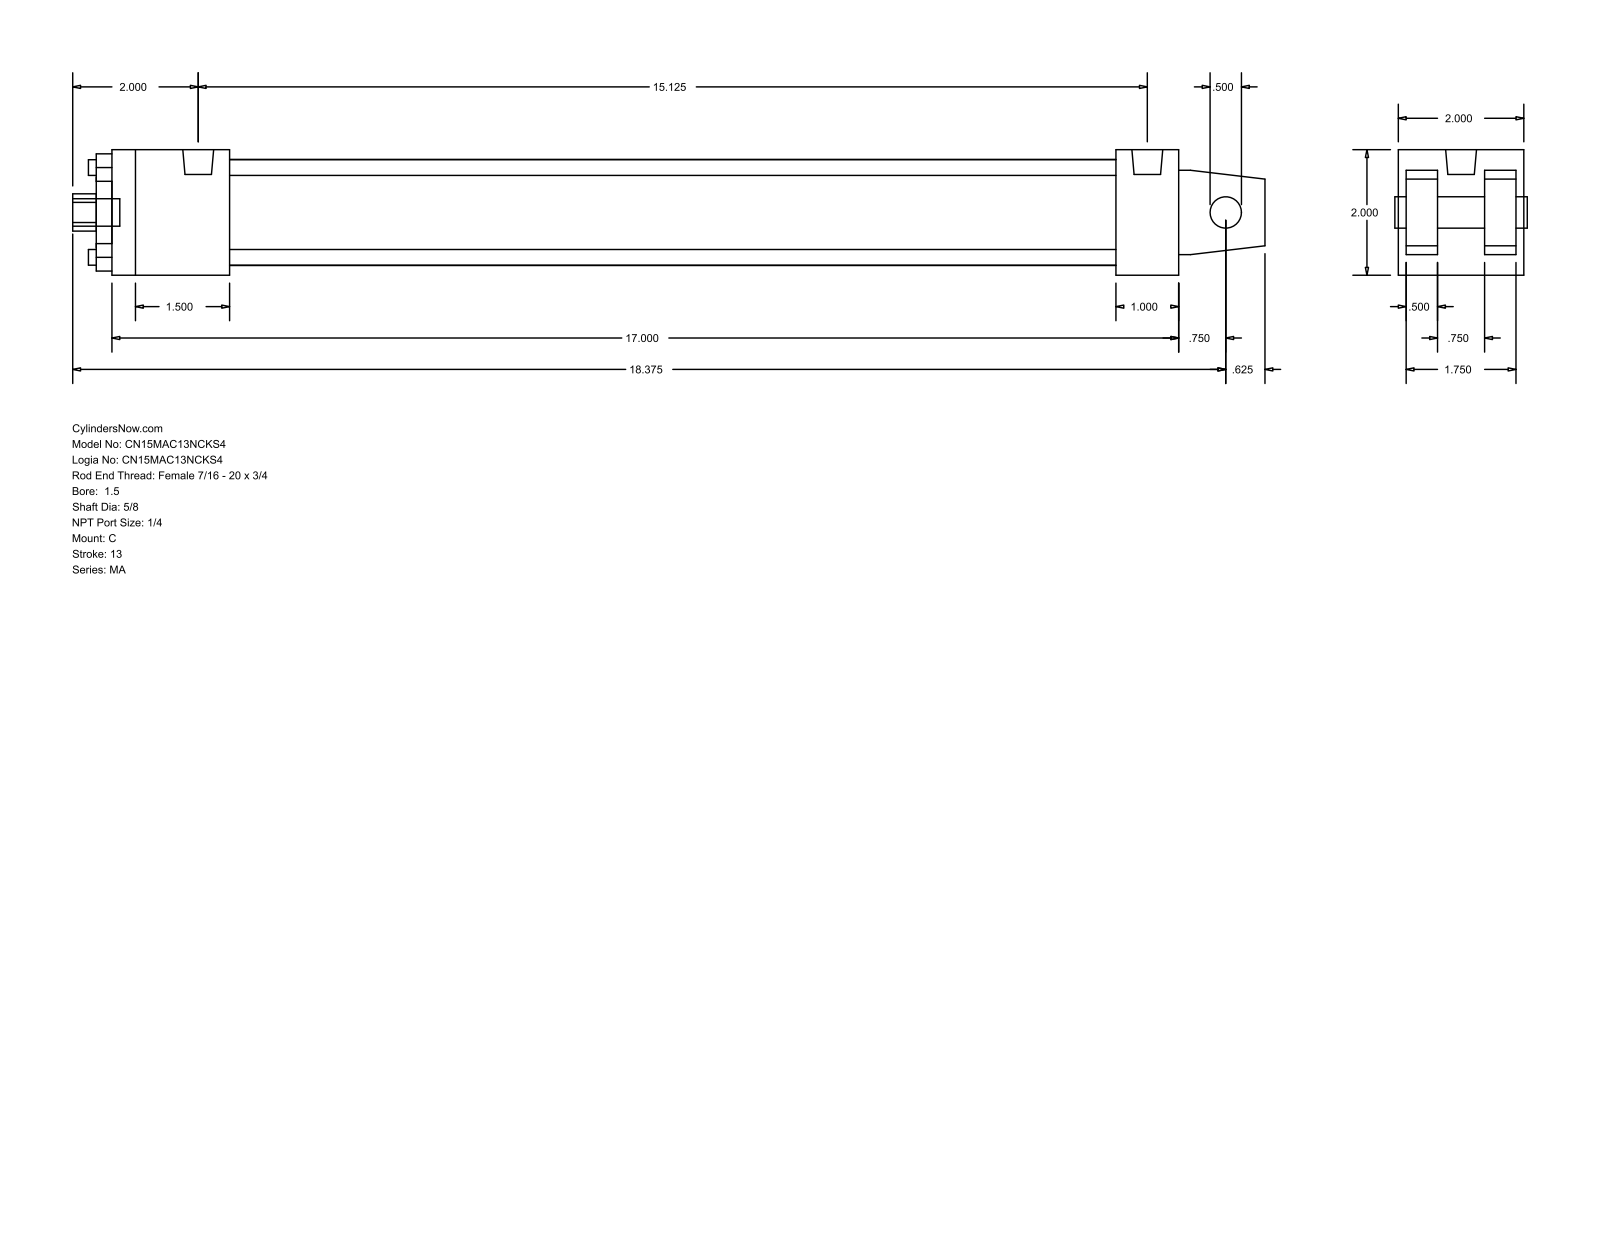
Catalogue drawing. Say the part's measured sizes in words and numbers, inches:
The part is named "MA_C__0150_0.625". Its 3-D file was written by "GSSL Pune (CONFIG_CONTROL_DESIGN)". It is 0 solids with 103 faces: 76 planar, 27 cylindrical and 0 other. Overall it measures 19 by 2 by 2 inches. Round holes: 4 of diameter 0.25, 1 of diameter 0.5, 1 of diameter 0.625, 1 of diameter 1.125, 1 of diameter 1.69. Round bosses or shafts: 4 of diameter 0.313, 2 of diameter 0.492, 1 of diameter 0.437. Partial cylindrical surfaces (rounded edges, fillets, slot ends): 1 of radius 0.297. The main face-to-face distances are 2, 0.5, 0.125, 0.625, 1.375, 1.875, 1.25, 17, 16, 1. The hole center spacings are 1.011, 1.43, 2.022.
